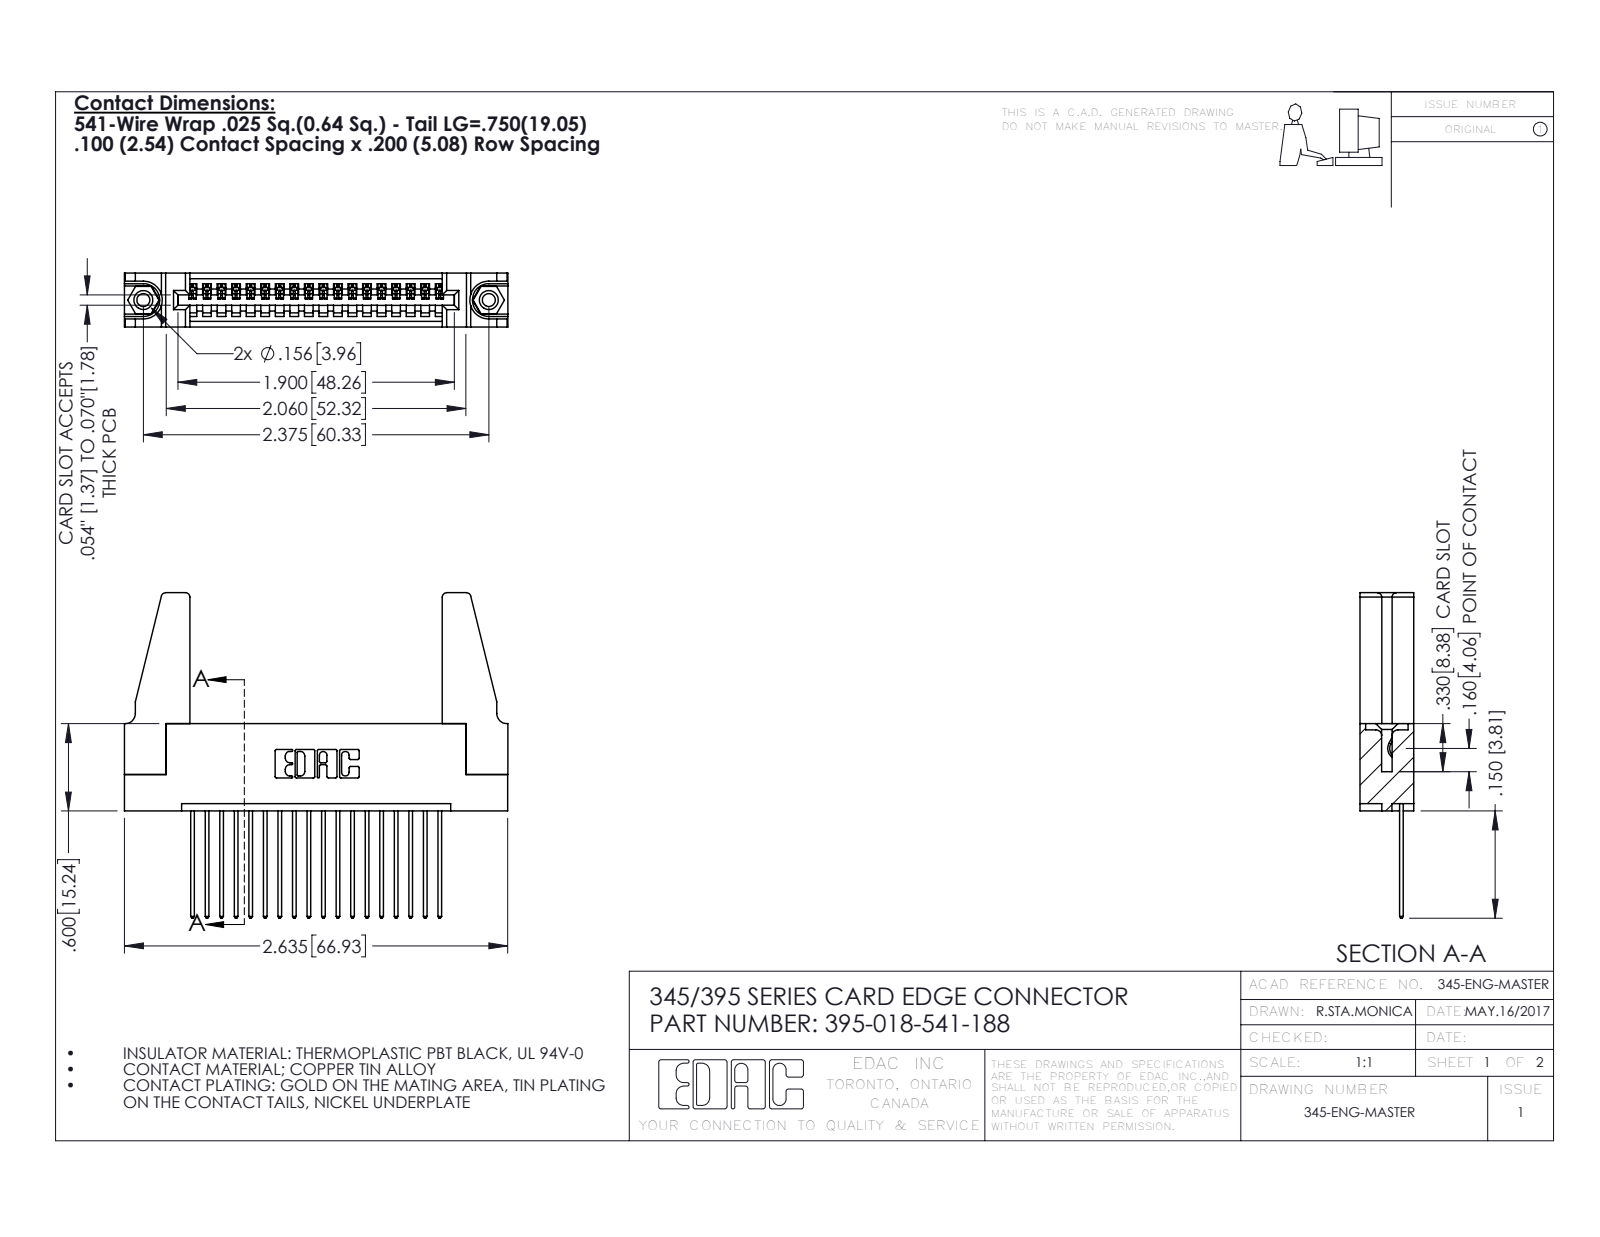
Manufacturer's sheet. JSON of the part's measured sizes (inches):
{"part_name": "395-018-541-188; 345-292-001_345-293-141; 345-220-078_345-220-088; 345 Part_Flush Mounting Lugs - 0.156 Dia-TH (+1 more)", "step_written_by": "SolidWorks 2016 (CONFIG_CONTROL_DESIGN)", "units": "inches", "bodies": {"solids": 23, "faces": 1294, "planar": 872, "cylindrical": 406, "other": 16}, "overall_size": [2.636, 2.237, 0.37], "volume_in3": 0.578, "surface_area_in2": 17.7, "round_holes": [[0.089, 2], [0.125, 2], [0.156, 2], [0.064, 1]], "round_bosses_or_shafts": [[0.155, 2]], "partial_cylinders_radius": [[0.006, 36], [0.01, 36], [0.01, 22], [0.03, 8], [0.007, 6], [0.031, 6], [0.026, 3], [0.031, 2]], "face_to_face_distances": [0.072, 0.37, 0.298, 0.2, 0.098, 0.272, 0.025, 0.225, 0.15, 0.148], "hole_center_spacings": [0.27, 2.141, 2.375]}
